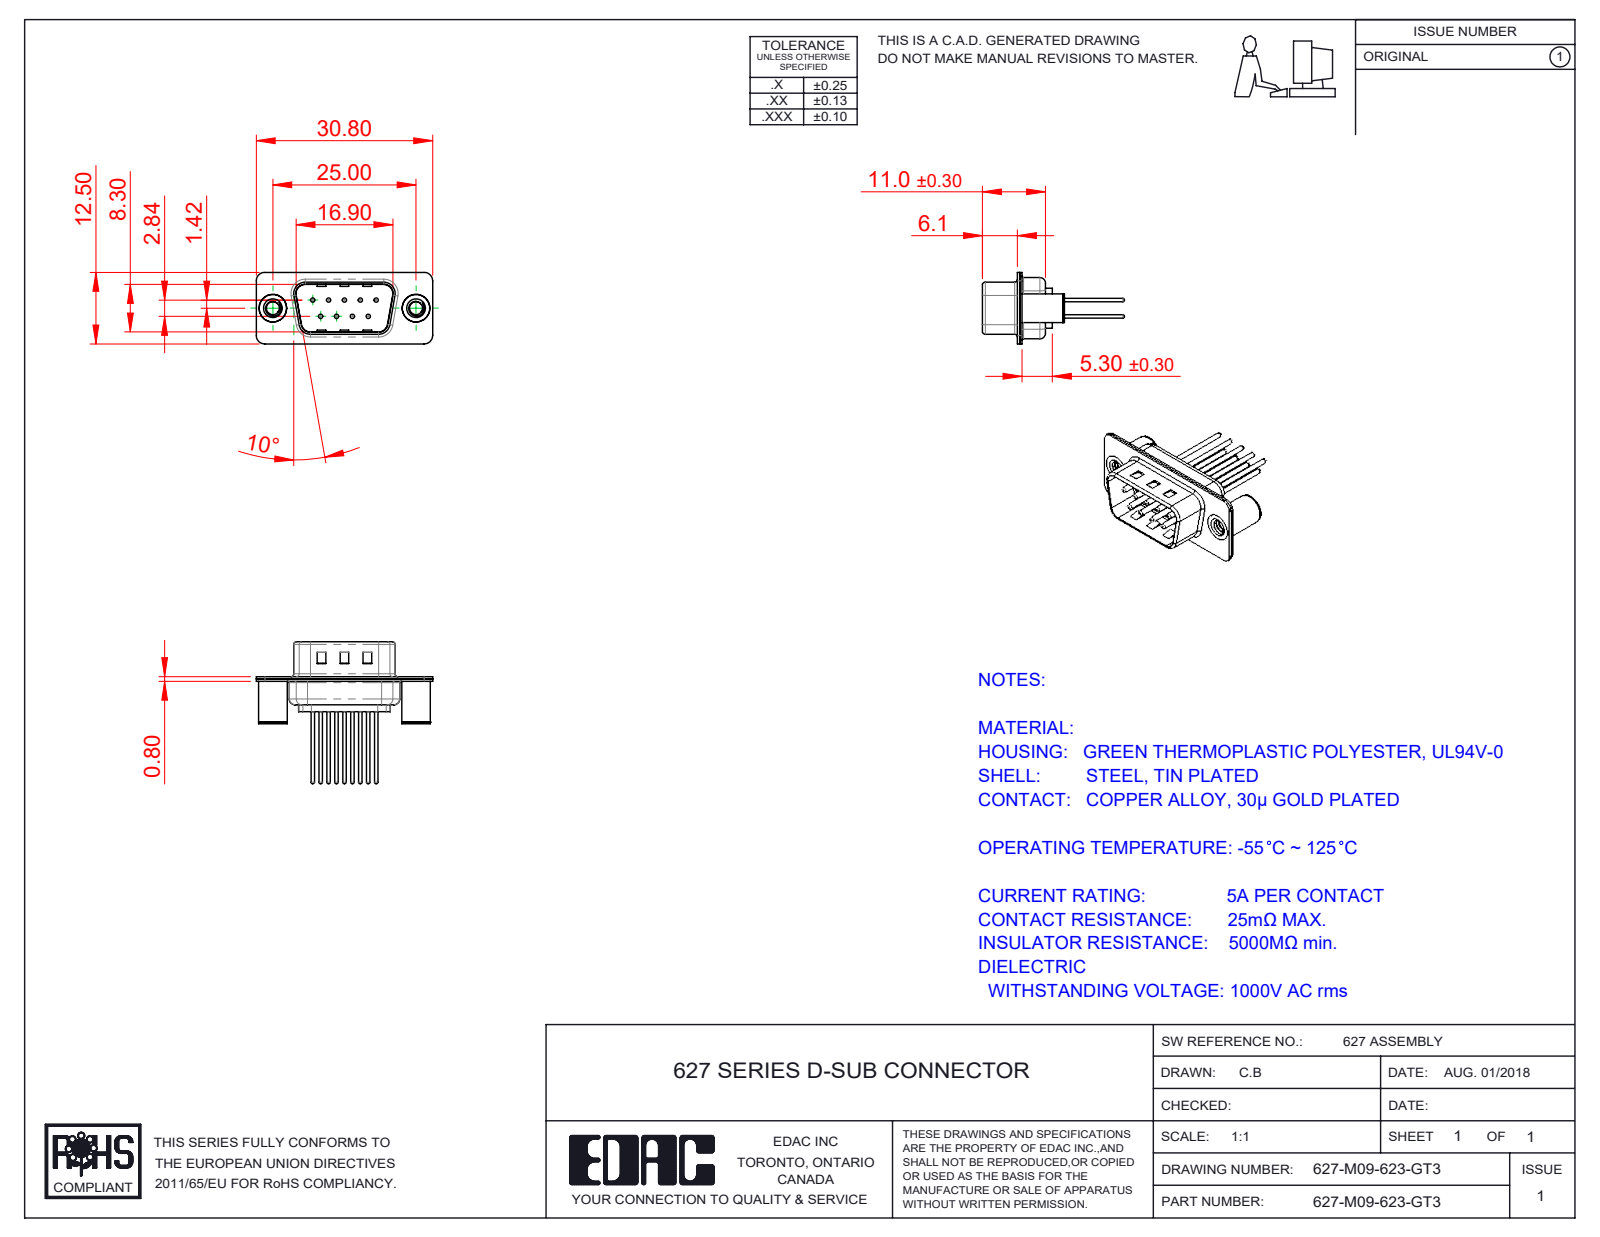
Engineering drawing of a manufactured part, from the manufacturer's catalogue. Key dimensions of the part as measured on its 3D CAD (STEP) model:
Part name (STEP PRODUCT): 627M 4-40 Threaded Board Spacer; 627M Housing_09 Contacts; 627M Contact Row 1_23; 627-M09-623-GT3 (+3 more)
STEP written by: SolidWorks 2020 (CONFIG_CONTROL_DESIGN)
Units: millimetres
Bodies: 14 solids, 671 faces (170 planar, 279 cylindrical, 222 other)
Overall size (bounding box): 30.8 × 24.77 × 12.5
Volume: 1 450 mm³ · Surface area: 3 949 mm²
Round holes (diameter × count): ⌀0.75 ×9, ⌀1.6 ×9, ⌀2 ×9, ⌀2.26 ×2, ⌀3.26 ×2, ⌀4 ×2, ⌀4.8 ×2
Round bosses / shafts (diameter × count): ⌀1.5 ×9, ⌀0.6 ×9, ⌀5 ×2, ⌀4.9 ×2
Partial cylindrical surfaces — rounded edges, fillets, slot ends (radius × count): R1.5 ×16, R2 ×12, R0.5 ×8, R1.6 ×8, R0.25 ×4, R0.6 ×4, R0.65 ×4, R0.9 ×4
Main face-to-face distances: 0.4, 0.8, 9.5, 9.1, 8.7, 0.65, 9.9, 1.2, 5.3, 6.1
Hole centre spacings: 3.16, 2.77, 5.54, 5.03, 5.04, 8.31, 7.1, 7.48
